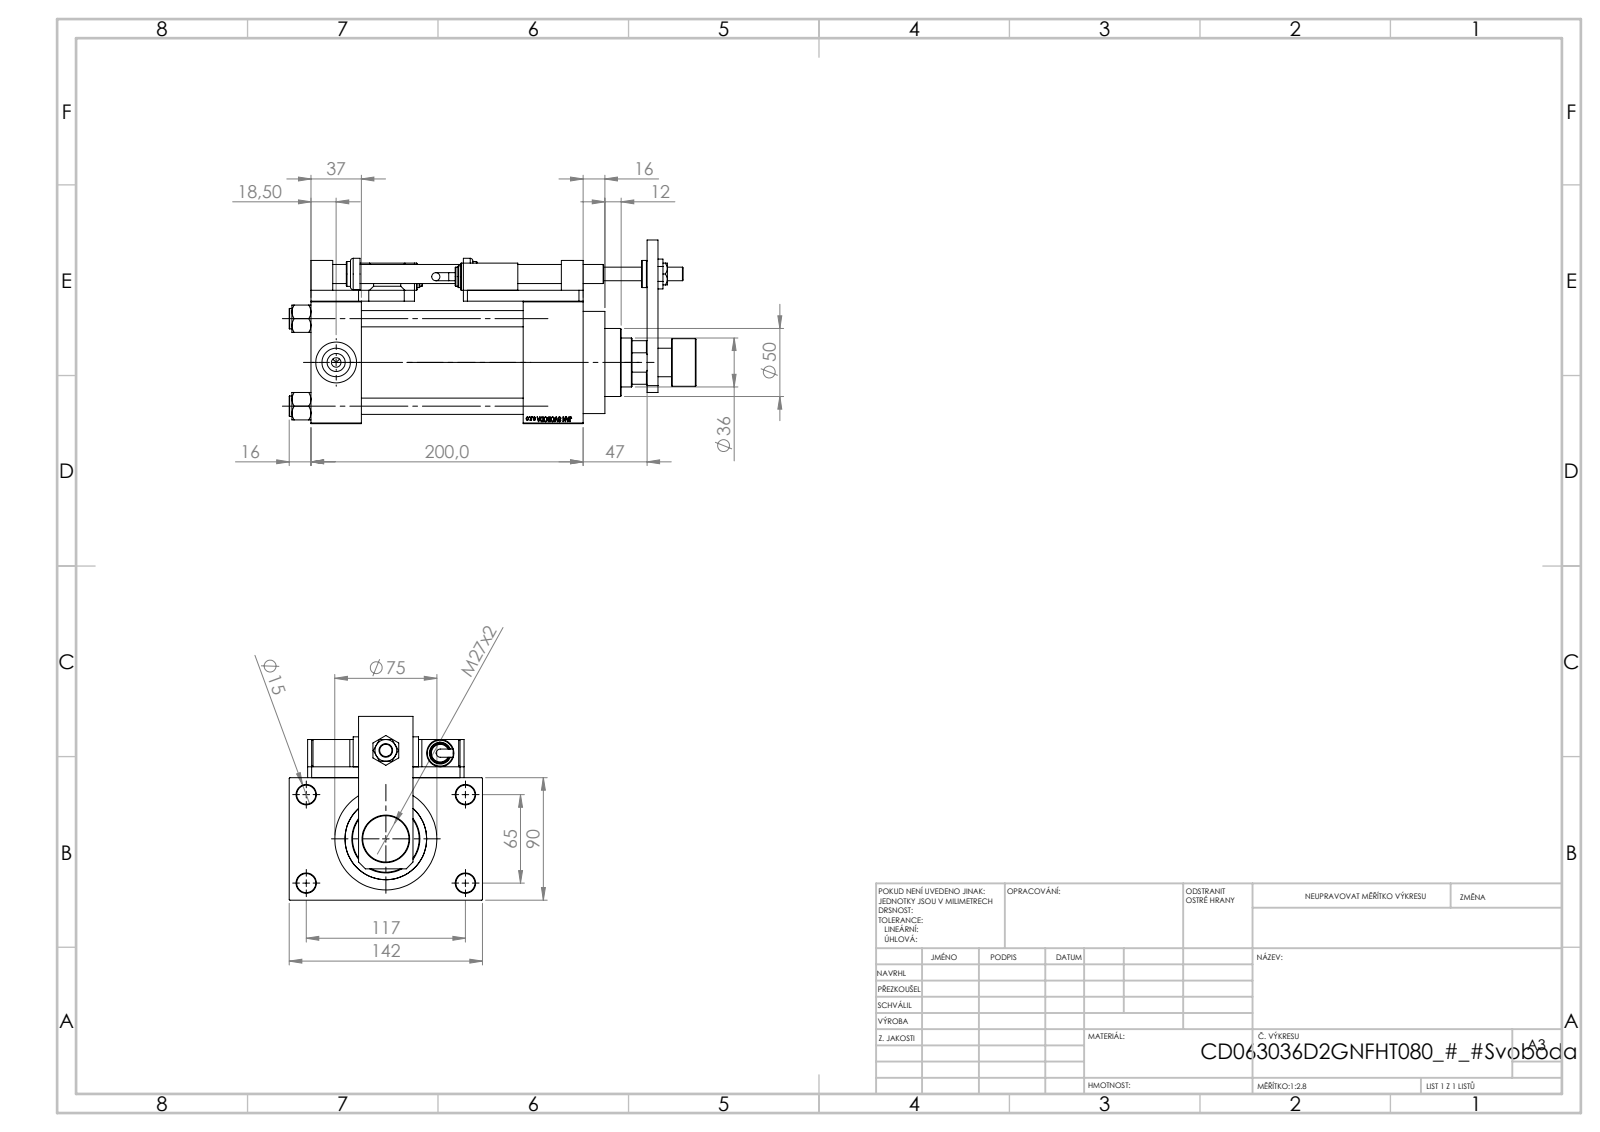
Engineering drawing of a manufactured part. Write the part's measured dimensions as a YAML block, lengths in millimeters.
part_name: "V215CD_SWITCH_Q_PODLOZKA_FRONT; V215CD_SWITCH_Q_NUT; V215CD_SWITCH_Q_BLOK; V215CD_VCP_D (+7 more)"
step_written_by: "SolidWorks 2019 (CONFIG_CONTROL_DESIGN)"
units: millimeters
bodies: {solids: 26, faces: 1398, planar: 646, cylindrical: 167, other: 585}
overall_size: [299, 142, 135]
volume: 1531000
surface_area: 342377
round_holes:
  - {diameter: 14, count: 5}
  - {diameter: 8.5, count: 4}
  - {diameter: 12, count: 4}
  - {diameter: 13.5, count: 4}
  - {diameter: 7, count: 3}
  - {diameter: 20.96, count: 3}
  - {diameter: 30, count: 3}
  - {diameter: 10, count: 1}
  - {diameter: 25.5, count: 1}
  - {diameter: 27, count: 1}
  - {diameter: 36, count: 1}
  - {diameter: 39, count: 1}
round_bosses_or_shafts:
  - {diameter: 15, count: 4}
  - {diameter: 20, count: 3}
  - {diameter: 16, count: 2}
  - {diameter: 14, count: 2}
  - {diameter: 6, count: 2}
  - {diameter: 75, count: 1}
  - {diameter: 69, count: 1}
  - {diameter: 35, count: 1}
partial_cylinders:
  - {radius: 7.5, count: 4}
face_to_face_distances: [8, 90, 44, 37, 200, 98, 163, 156, 119, 116]
hole_center_spacings: [66.92, 26.35, 45.47, 64.3, 69.81, 90.65, 111.34, 65]
